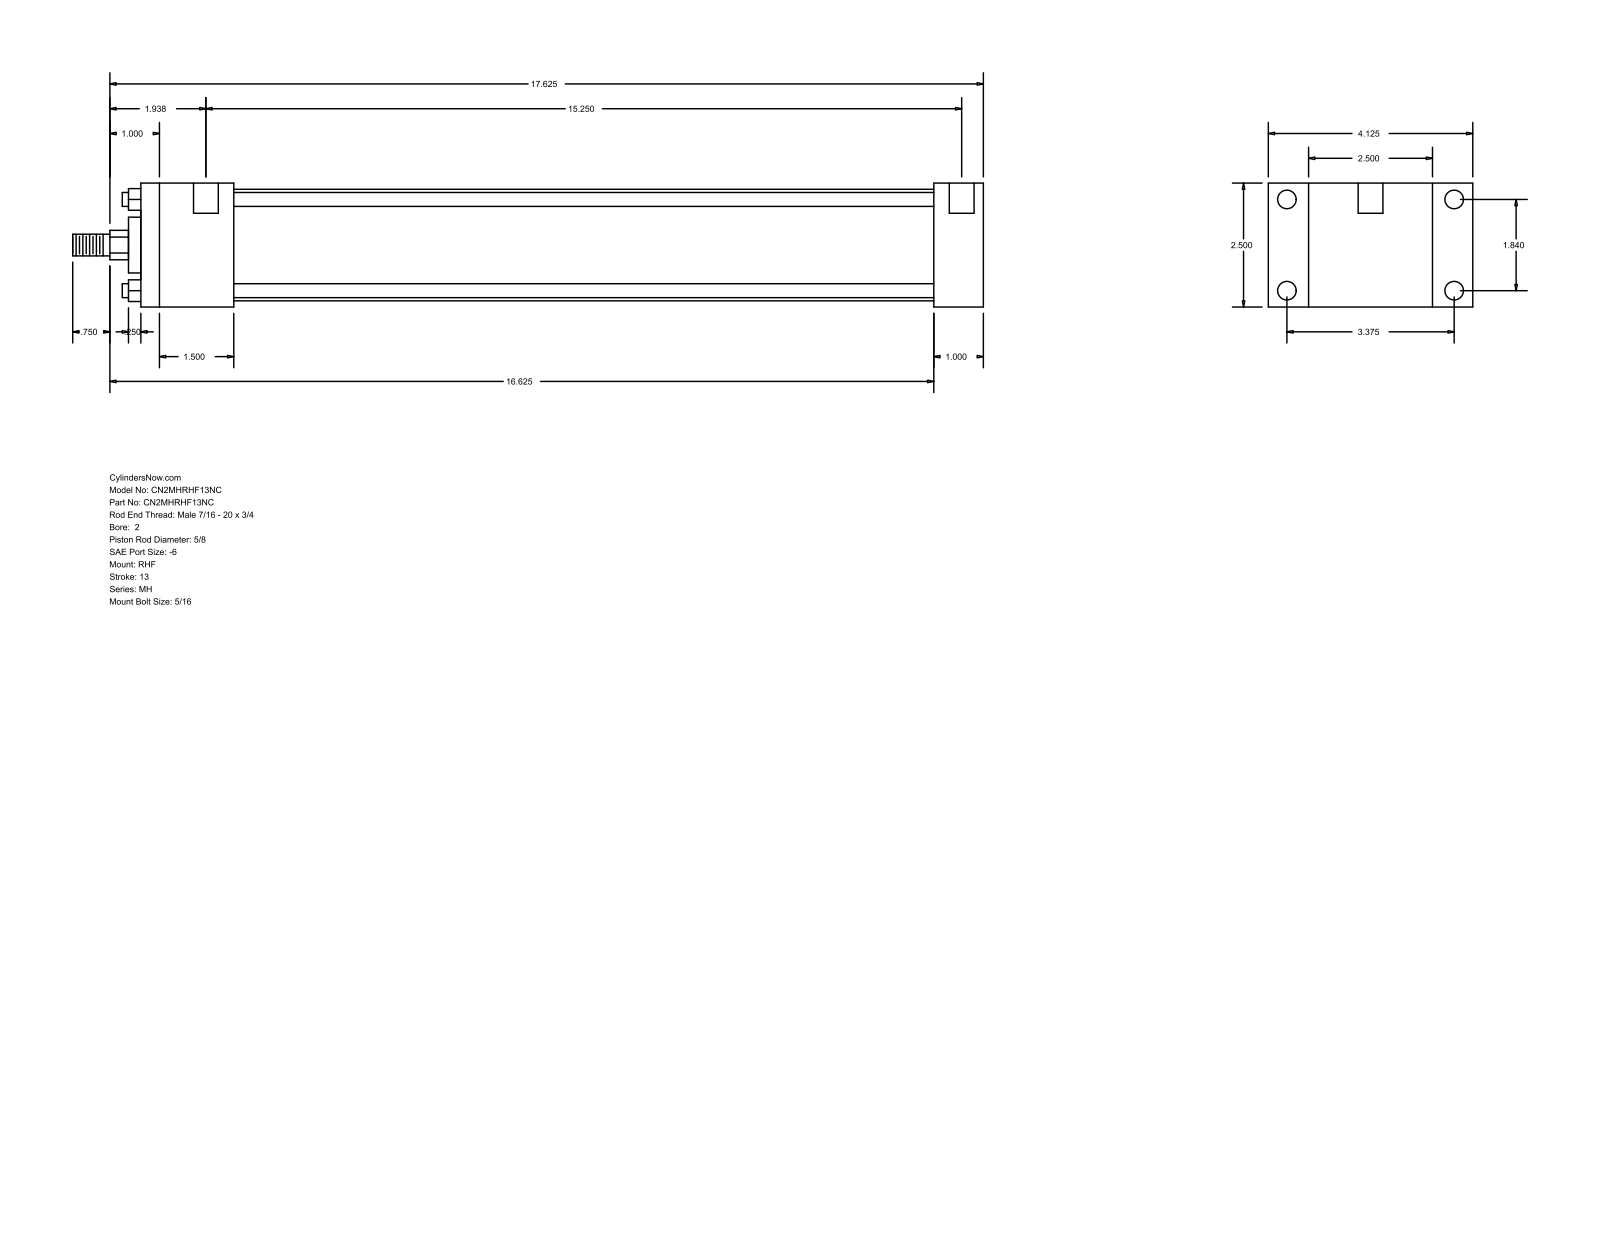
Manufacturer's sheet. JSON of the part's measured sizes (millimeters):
{"part_name": "MH_RHF__0200_0.625", "step_written_by": "GSSL Pune (CONFIG_CONTROL_DESIGN)", "units": "millimeters", "bodies": {"solids": 0, "faces": 88, "planar": 60, "cylindrical": 28, "other": 0}, "overall_size": [466.73, 104.78, 63.5], "round_holes": [[5.56, 4], [9.53, 4], [12.7, 2]], "round_bosses_or_shafts": [[7.14, 4], [57.15, 1], [28.57, 1], [15.88, 1], [11.11, 1]], "partial_cylinders_radius": [[7.54, 1]], "face_to_face_distances": [63.5, 25.41, 20.64, 84.14, 406.39, 431.8, 104.78, 47.62, 358.77, 384.18], "hole_center_spacings": [46.74, 85.72, 97.63, 395.29, 3.18, 4.76, 387.35, 390.53]}
